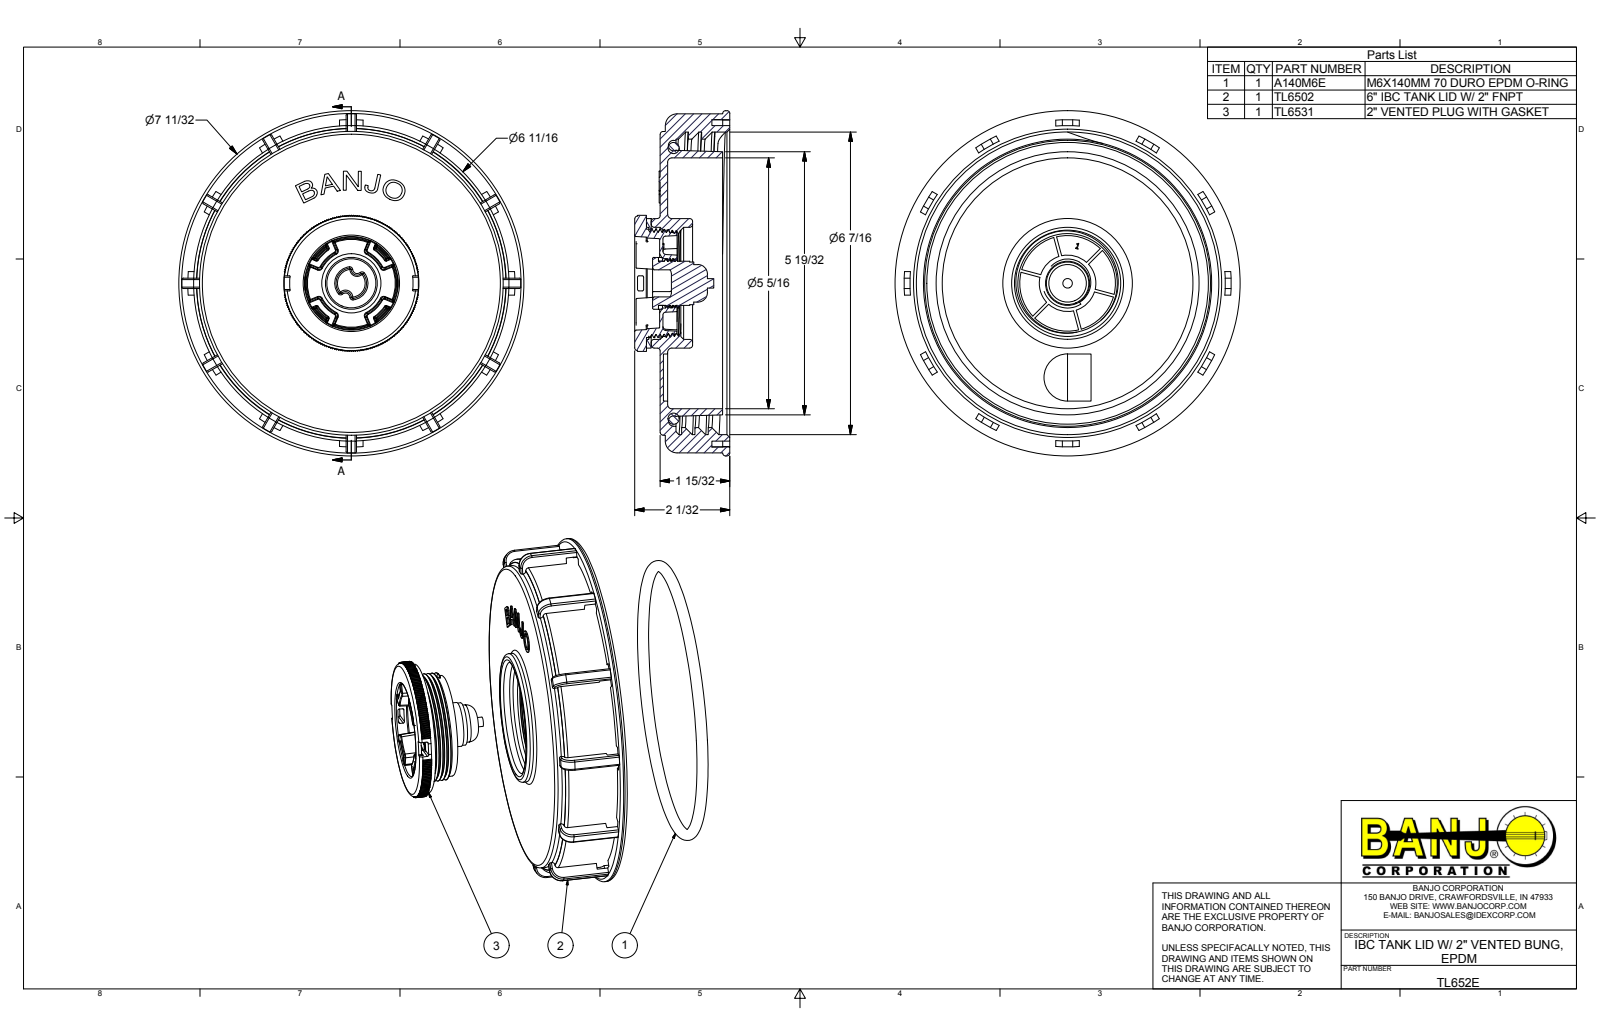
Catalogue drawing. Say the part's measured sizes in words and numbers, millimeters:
The part is named "TL6502; A140M6E; 200MPT; 200MPTG (+3 more)". Its 3-D file was written by "Autodesk Inventor 2016 (AUTOMOTIVE_DESIGN)". It is 6 solids with 1696 faces: 787 planar, 522 cylindrical and 387 other. Overall it measures 186.18 by 186.18 by 51.31 millimeters. Its volume is 323 486 cubic millimeters and its surface area 166 785 square millimeters. Round holes: 1 of diameter 23.84, 1 of diameter 58.42, 1 of diameter 60.45, 1 of diameter 135.32, 1 of diameter 154.18, 1 of diameter 155.57, 1 of diameter 163.19. Round bosses or shafts: 1 of diameter 186.18, 1 of diameter 170.18, 1 of diameter 163.83, 1 of diameter 69.85, 1 of diameter 27.94, 1 of diameter 23.79, 1 of diameter 22.96, 1 of diameter 20.22. Partial cylindrical surfaces (rounded edges, fillets, slot ends): 52 of radius 0.76, 36 of radius 0.38, 12 of radius 6.35, 2 of radius 3.17, 1 of radius 8.26, 1 of radius 12.7, 1 of radius 33.27, 1 of radius 36.32. The main face-to-face distances are 4.06, 37.59, 33.53, 8.89, 33.78, 29.72, 3.81, 7.37, 6.35, 11.43.
